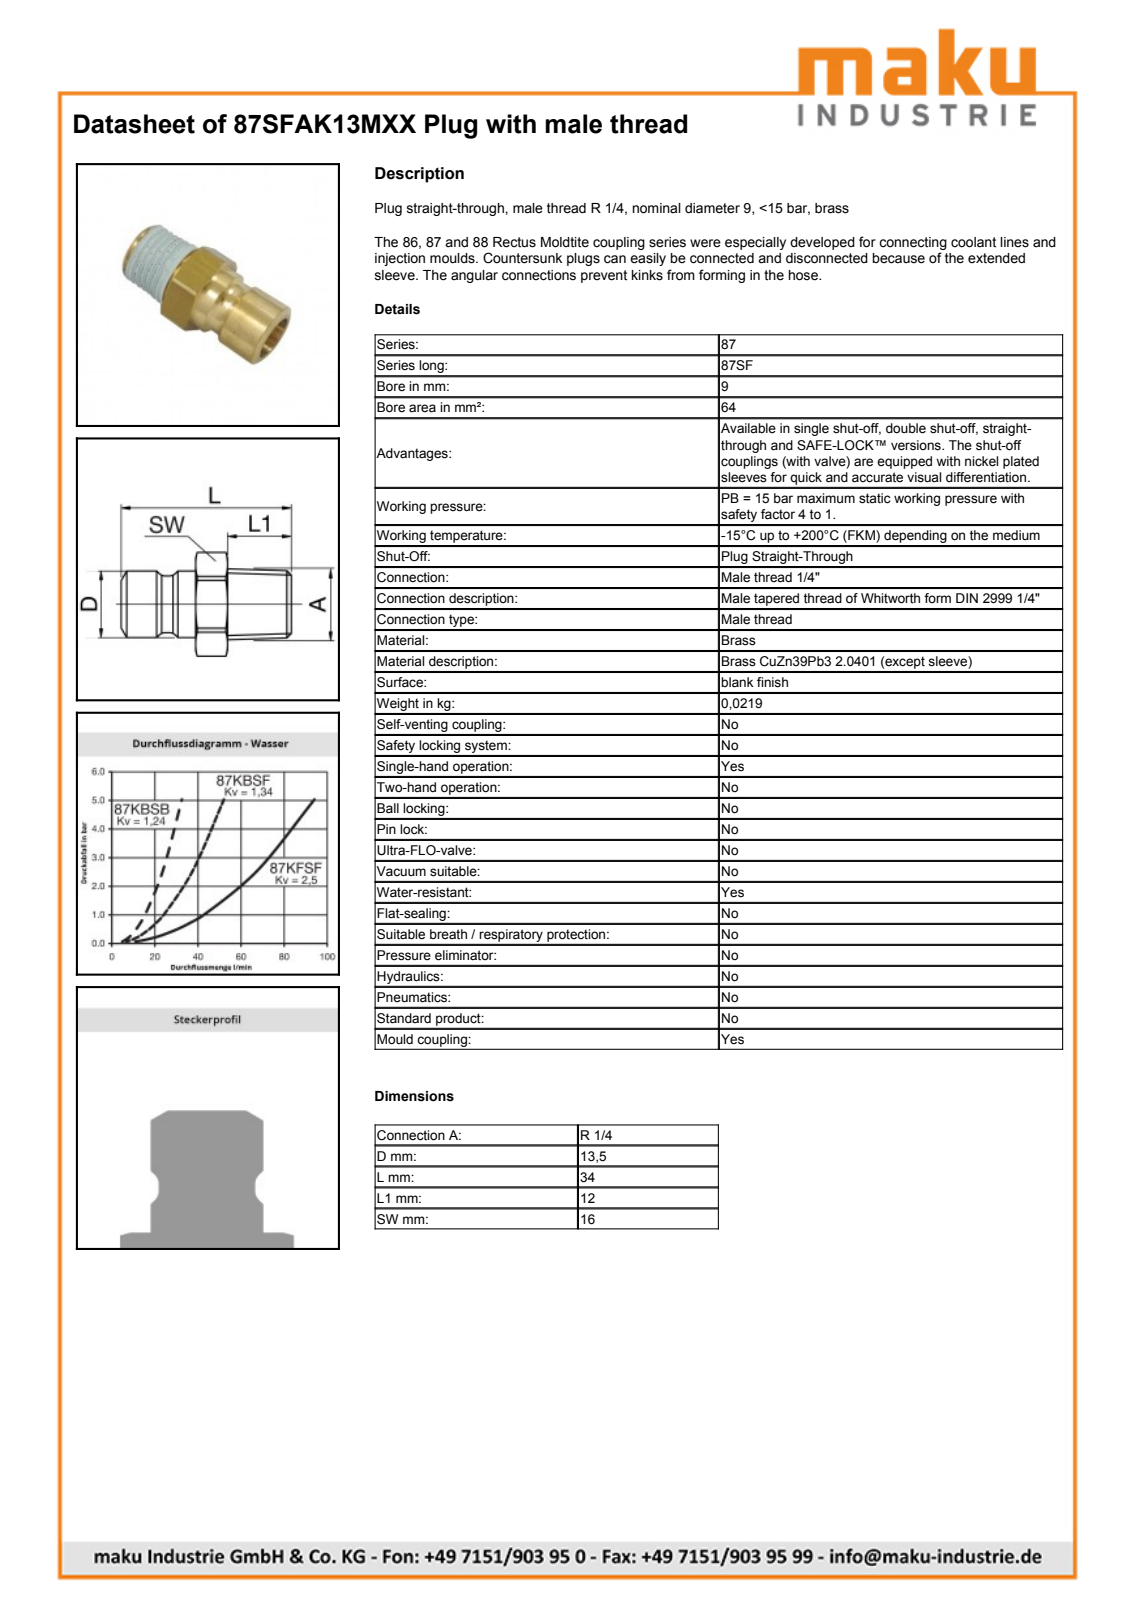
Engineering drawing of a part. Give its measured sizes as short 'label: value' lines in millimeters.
name: D106721
written by: Autodesk Inventor 2011 (AUTOMOTIVE_DESIGN)
unit: mm
bodies: 1 solid, 39 faces (10 planar, 10 cylindrical, 19 other)
size: 34 × 18.05 × 16
volume: 2 884 mm³; area: 2 741 mm²
holes: 1× ⌀9.2
bosses: 1× ⌀13.5, 1× ⌀11.5
rounds: 1× R9.03
face distances: 16, 6.5, 15.5, 22, 34, 18.5, 12
